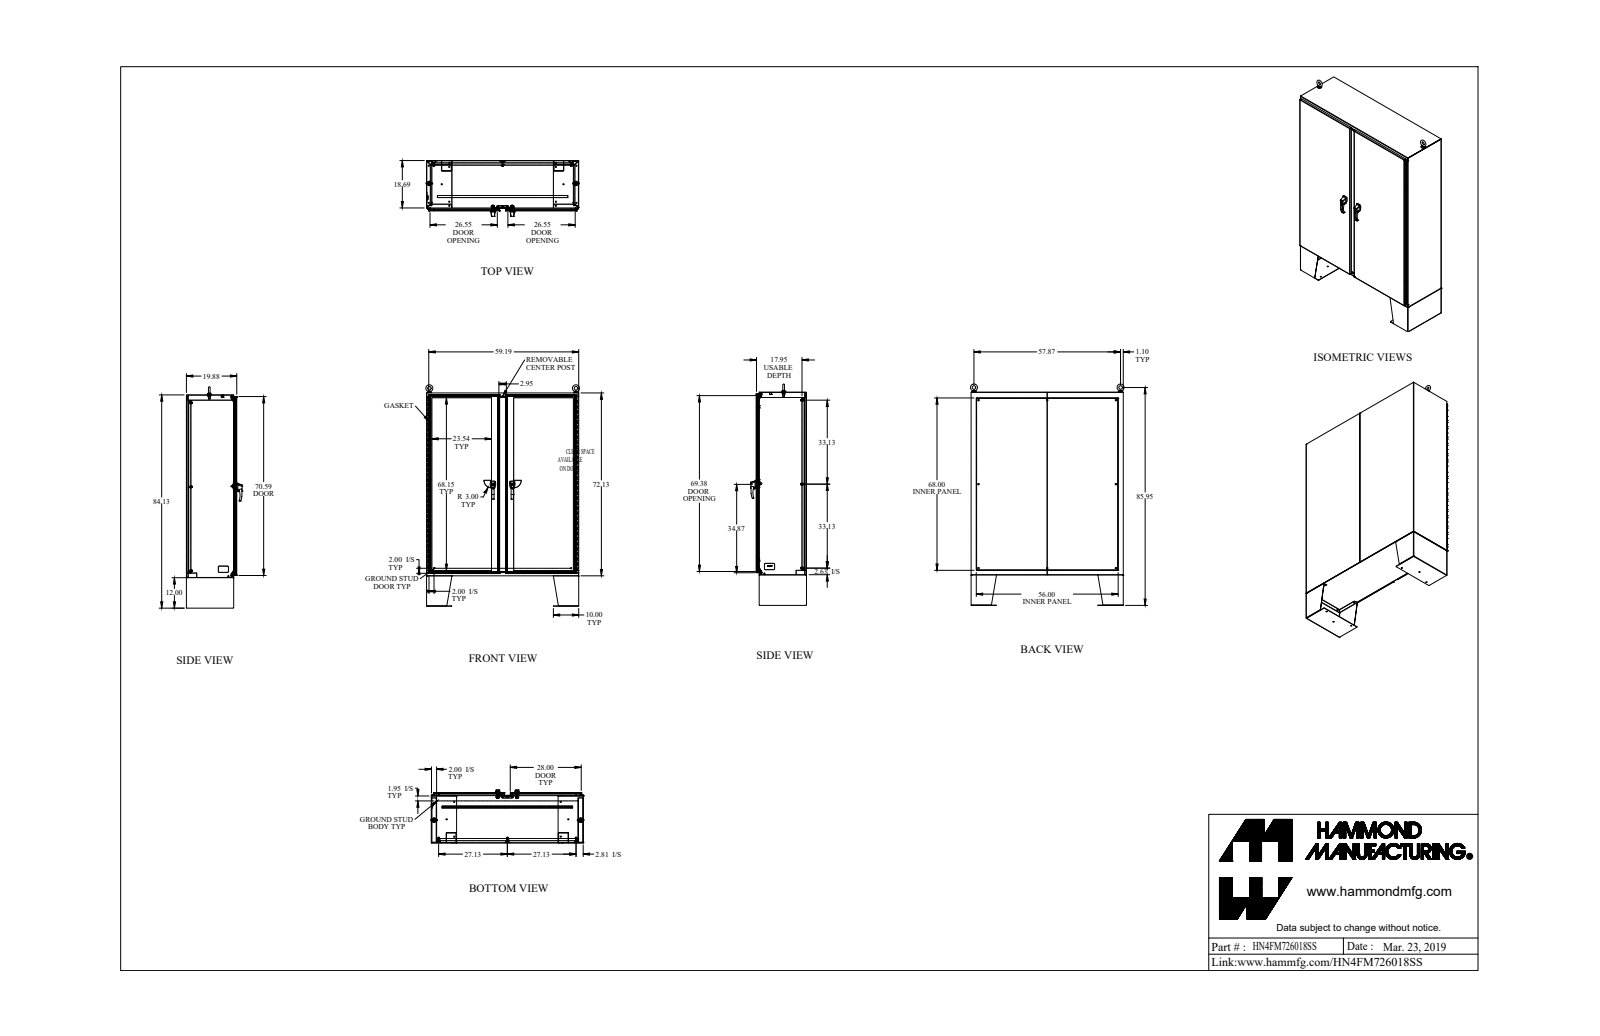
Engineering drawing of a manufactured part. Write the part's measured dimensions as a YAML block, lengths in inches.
part_name: "HN4FM726018SS"
step_written_by: "SolidWorks 2018 (AUTOMOTIVE_DESIGN)"
units: inches
bodies: {solids: 131, faces: 3990, planar: 1826, cylindrical: 1803, other: 361}
overall_size: [87.321, 60.607, 21.99]
volume: 2237
surface_area: 44903
round_holes:
  - {diameter: 0.304, count: 24}
  - {diameter: 0.437, count: 14}
  - {diameter: 0.25, count: 8}
  - {diameter: 0.307, count: 8}
  - {diameter: 0.35, count: 8}
  - {diameter: 0.563, count: 8}
  - {diameter: 0.445, count: 6}
  - {diameter: 0.257, count: 4}
  - {diameter: 0.28, count: 4}
  - {diameter: 0.281, count: 4}
  - {diameter: 0.313, count: 4}
  - {diameter: 0.39, count: 4}
round_bosses_or_shafts:
  - {diameter: 1, count: 12}
  - {diameter: 0.65, count: 8}
  - {diameter: 0.375, count: 8}
  - {diameter: 0.332, count: 8}
  - {diameter: 0.75, count: 4}
  - {diameter: 0.63, count: 4}
  - {diameter: 0.625, count: 4}
  - {diameter: 0.44, count: 4}
partial_cylinders:
  - {radius: 0.125, count: 43}
  - {radius: 0.5, count: 33}
  - {radius: 0.018, count: 32}
  - {radius: 0.048, count: 29}
  - {radius: 0.143, count: 29}
  - {radius: 0.06, count: 28}
  - {radius: 0.03, count: 12}
  - {radius: 0.09, count: 12}
face_to_face_distances: [0.095, 19.78, 19.685, 0.125, 17.998, 19.875, 1.782, 1.687, 18.093, 1.657]
hole_center_spacings: [6, 12, 18, 24, 30, 36, 42, 1.61]
